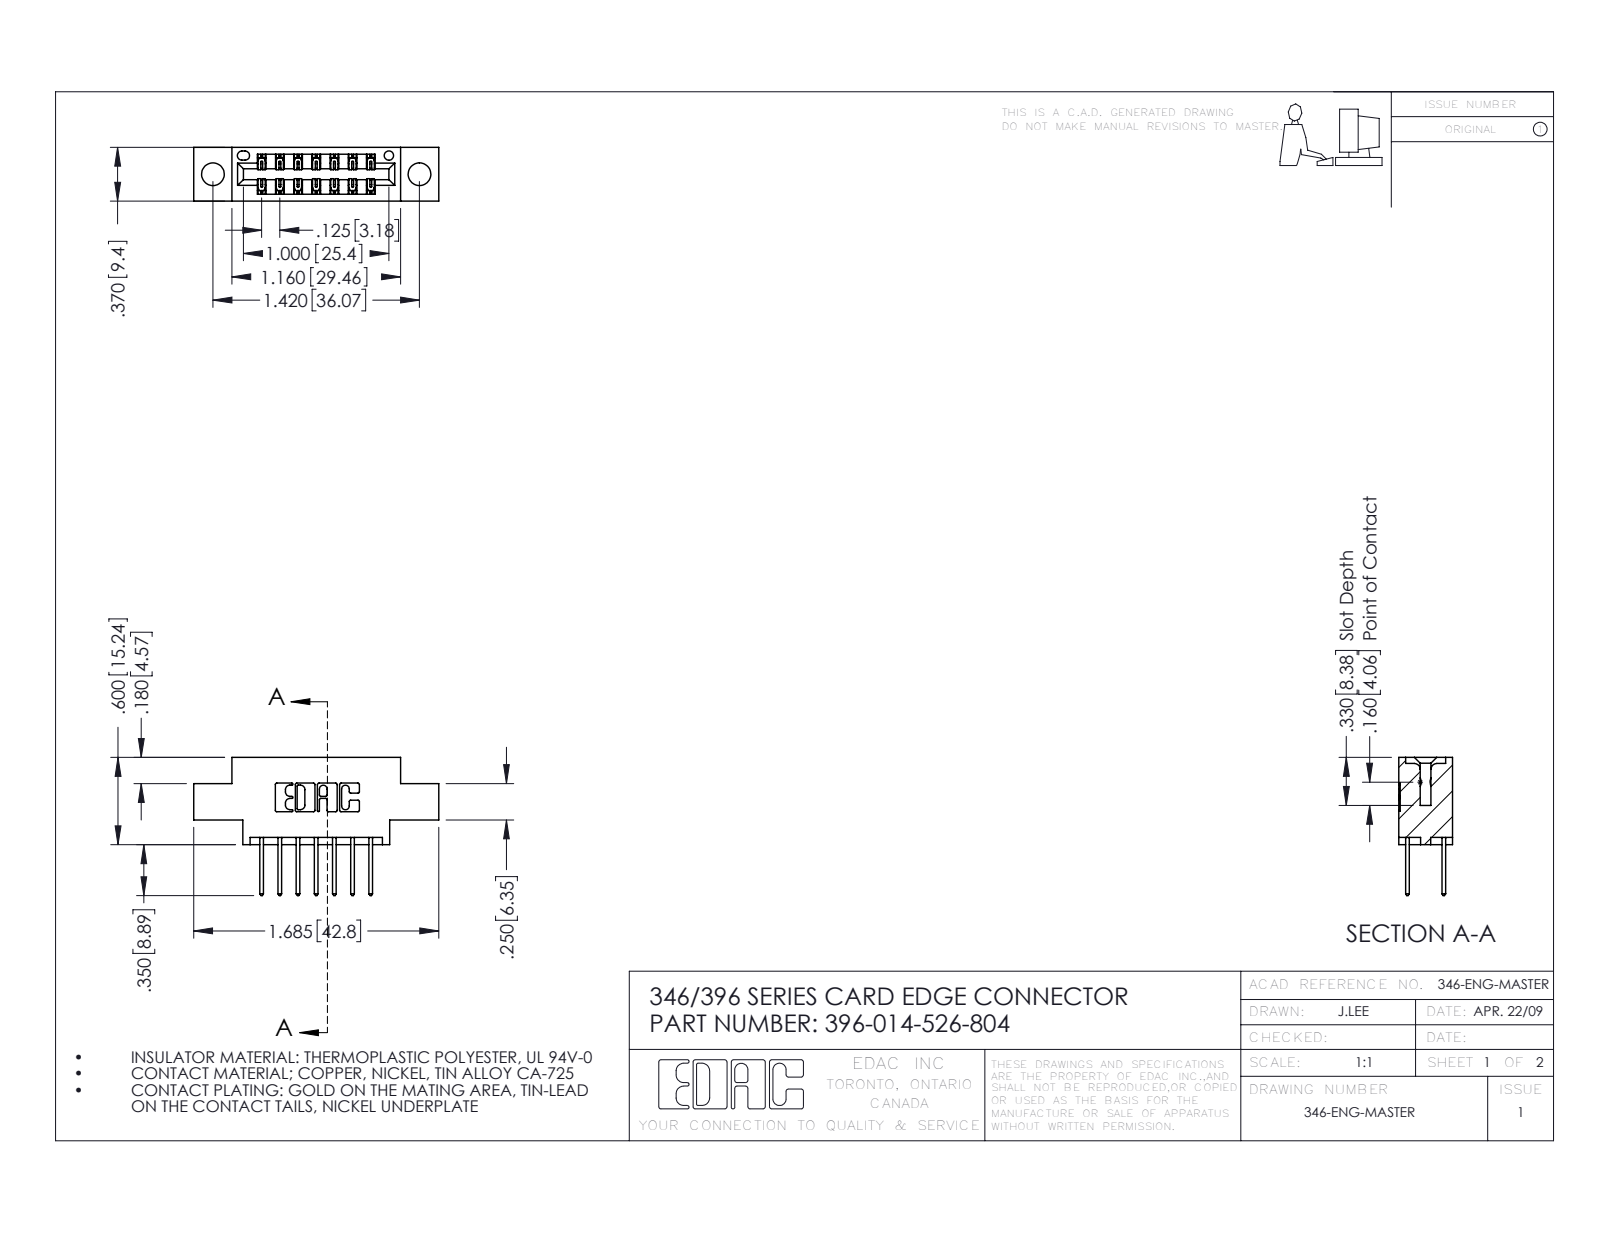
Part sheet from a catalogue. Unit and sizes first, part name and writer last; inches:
Units: inches
Overall size (bounding box): 1.685 × 0.95 × 0.37
Round holes (diameter × count): ⌀0.156 ×2, ⌀0.064 ×1
Partial cylindrical surfaces — rounded edges, fillets, slot ends (radius × count): R0.01 ×22, R0.006 ×21, R0.01 ×14, R0.007 ×6, R0.031 ×6, R0.026 ×3, R0.014 ×2, R0.022 ×2
Main face-to-face distances: 0.25, 0.37, 0.048, 0.322, 0.072, 0.298, 0.025, 0.275, 0.148, 0.222
Hole centre spacings: 0.246, 1.217, 1.42
Volume: 0.225 in³ · Surface area: 7.141 in²
Bodies: 15 solids, 854 faces (570 planar, 284 cylindrical, 0 other)
Part name (STEP PRODUCT): 346 Part_0.170 Offset - 0.156 Dia-TH; 345-292-001_345-293-126; 396-014-526-804
STEP written by: SolidWorks 2016 (CONFIG_CONTROL_DESIGN)
